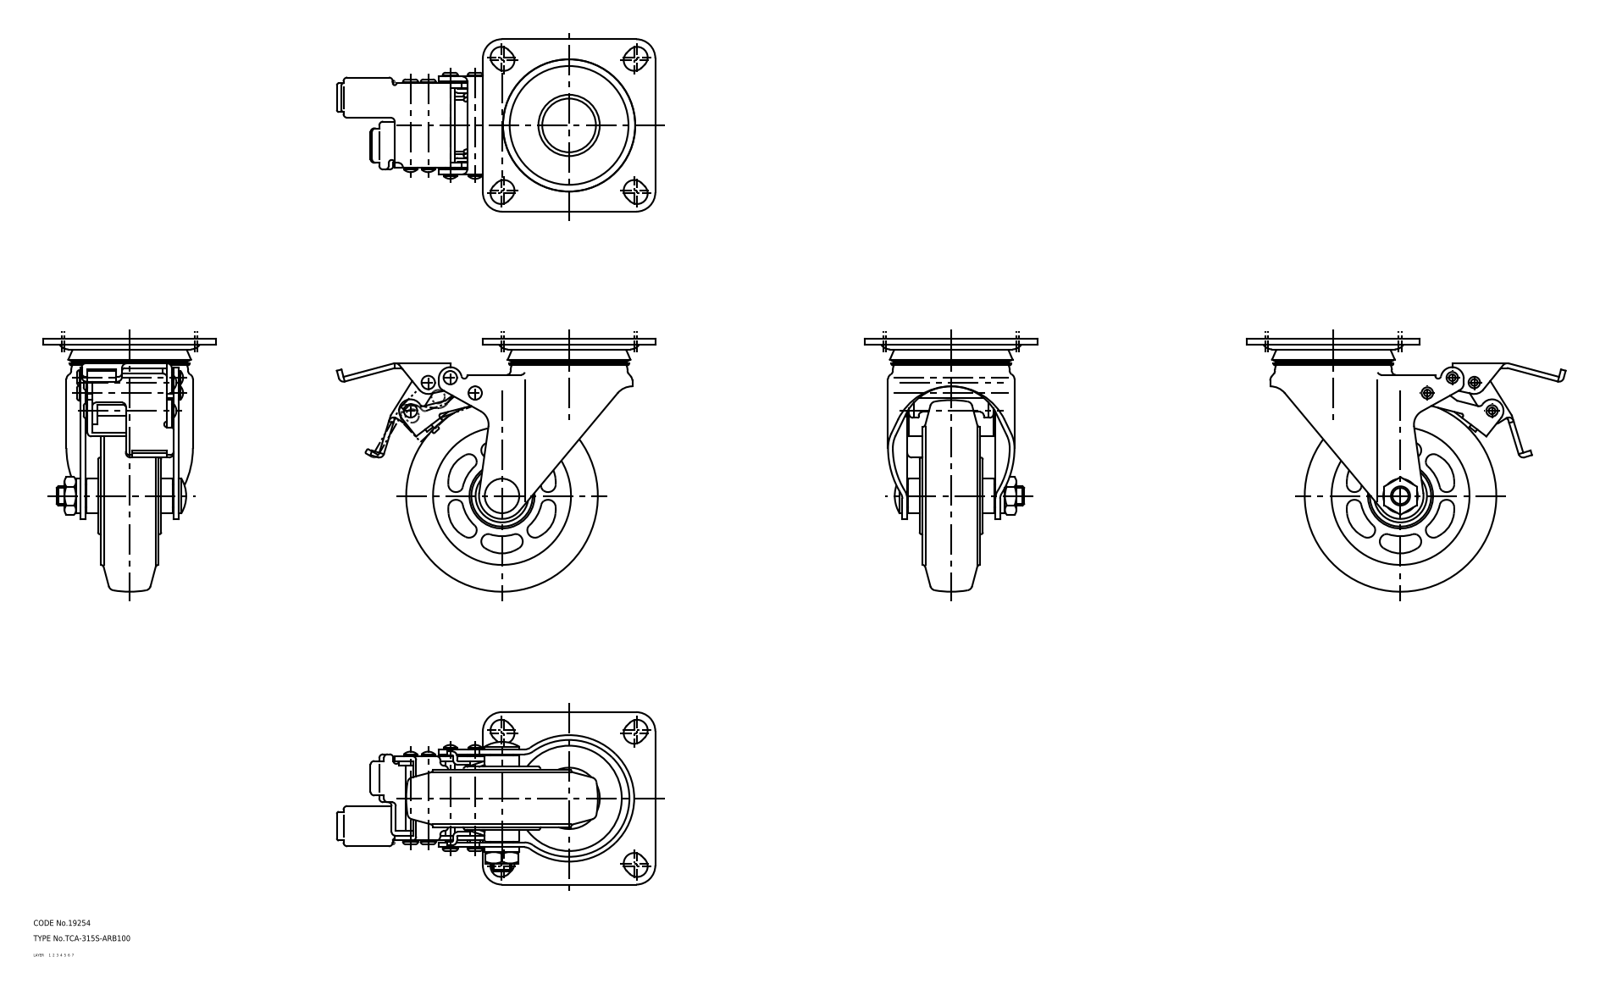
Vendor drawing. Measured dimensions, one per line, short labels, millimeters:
name: lever; wheel; mounting plate; main shaft (+2 more)
written by: CADfix (AUTOMOTIVE_DESIGN)
unit: mm
bodies: 6 solids, 502 faces (0 planar, 0 cylindrical, 502 other)
size: 166.18 × 132 × 90
volume: 300 888 mm³; area: 100 844 mm²
